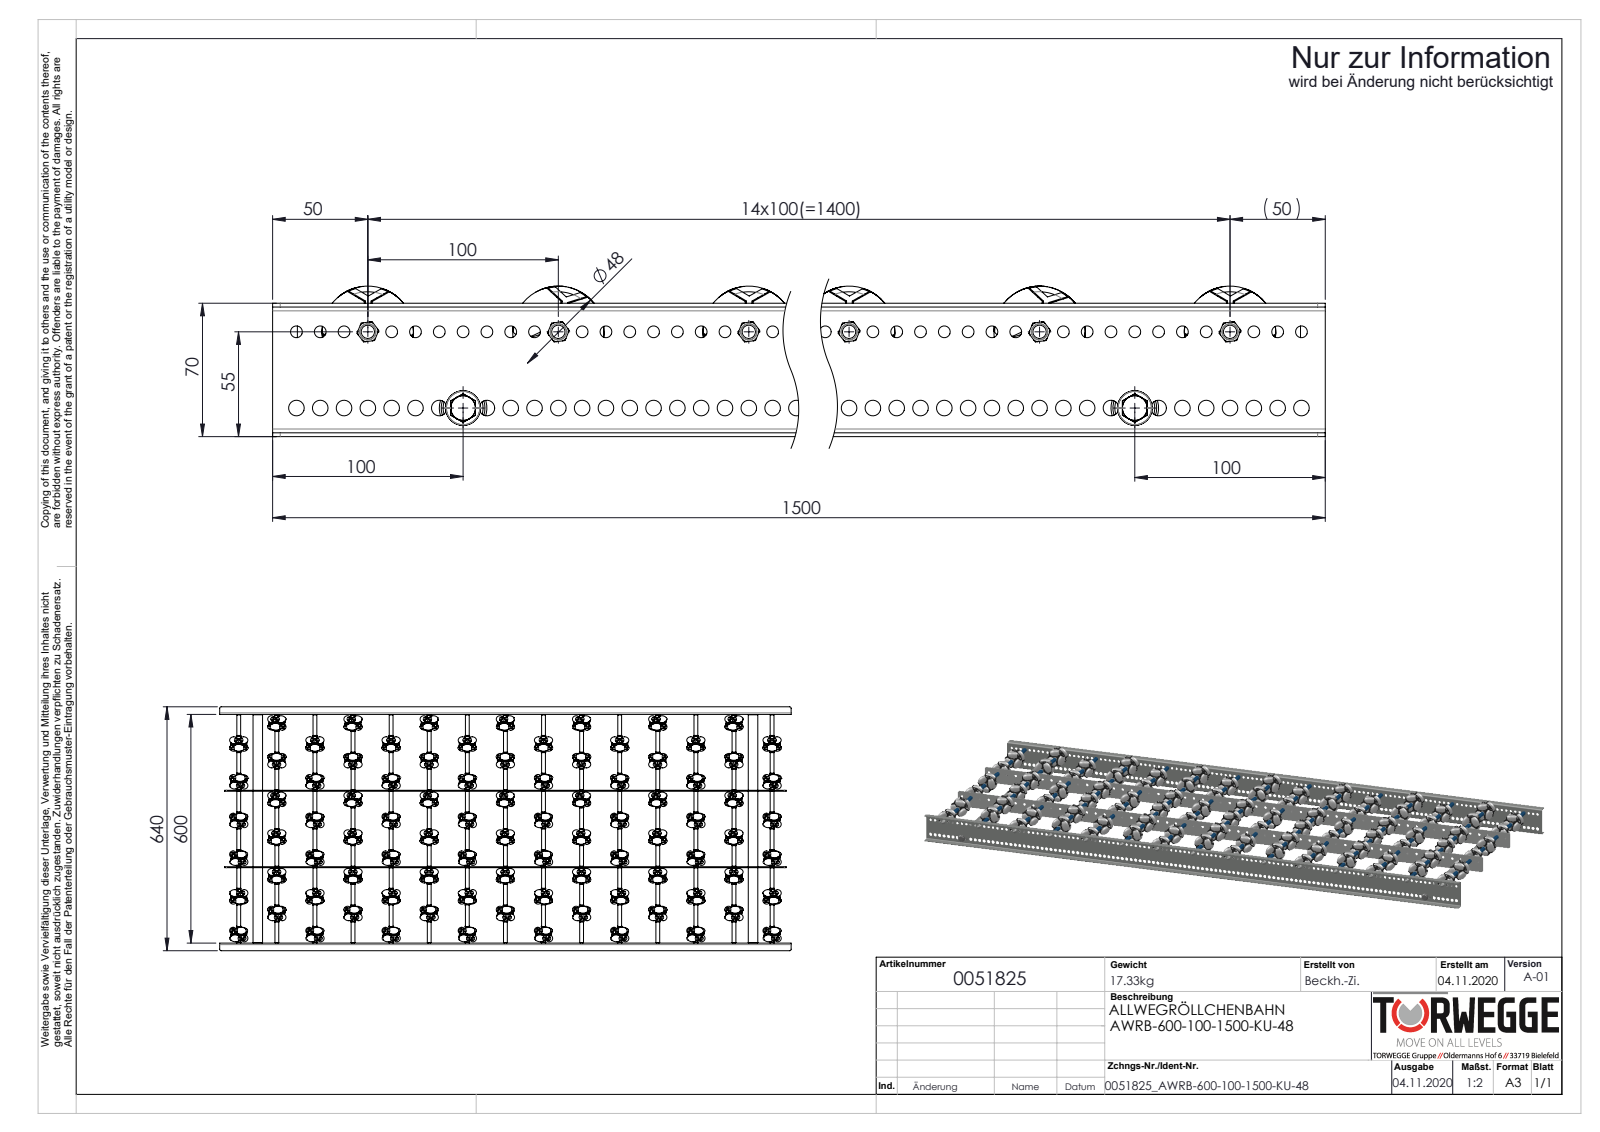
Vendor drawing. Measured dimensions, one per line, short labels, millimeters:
name: 0036819_SICHERUNGS-HUTMUTTER-DIN986-M6; 0027528_BUCHSE-HOHLNIETE ZU AWR48; 0019719_Gewindestange-M6_L=620; 0019730_Tragrollenrohr-Ø10x1,75KU_KFG_0019730_L=54 (+8 more)
written by: SolidWorks 2020 (AUTOMOTIVE_DESIGN)
unit: mm
bodies: 1499 solids, 26958 faces (9222 planar, 10762 cylindrical, 6974 other)
size: 1500 × 640 × 79
volume: 5 398 000 mm³; area: 3 779 000 mm²
holes: 540× ⌀3.7, 540× ⌀4.2, 119× ⌀6.2, 119× ⌀8.2, 59× ⌀6.5, 15× ⌀4.92, 15× ⌀8.4, 2× ⌀6.8, 2× ⌀21
bosses: 540× ⌀4, 461× ⌀3.7, 17× ⌀8, 15× ⌀47.1, 15× ⌀42, 15× ⌀11, 15× ⌀10, 15× ⌀7
rounds: 8× R4, 4× R2, 4× R5
face distances: 2, 602, 200.5, 2.5, 68, 600, 604, 399.6, 198, 203
hole spacings: 36.06, 36.05, 36.04, 36.07, 8, 169.07, 6.2, 81.84
